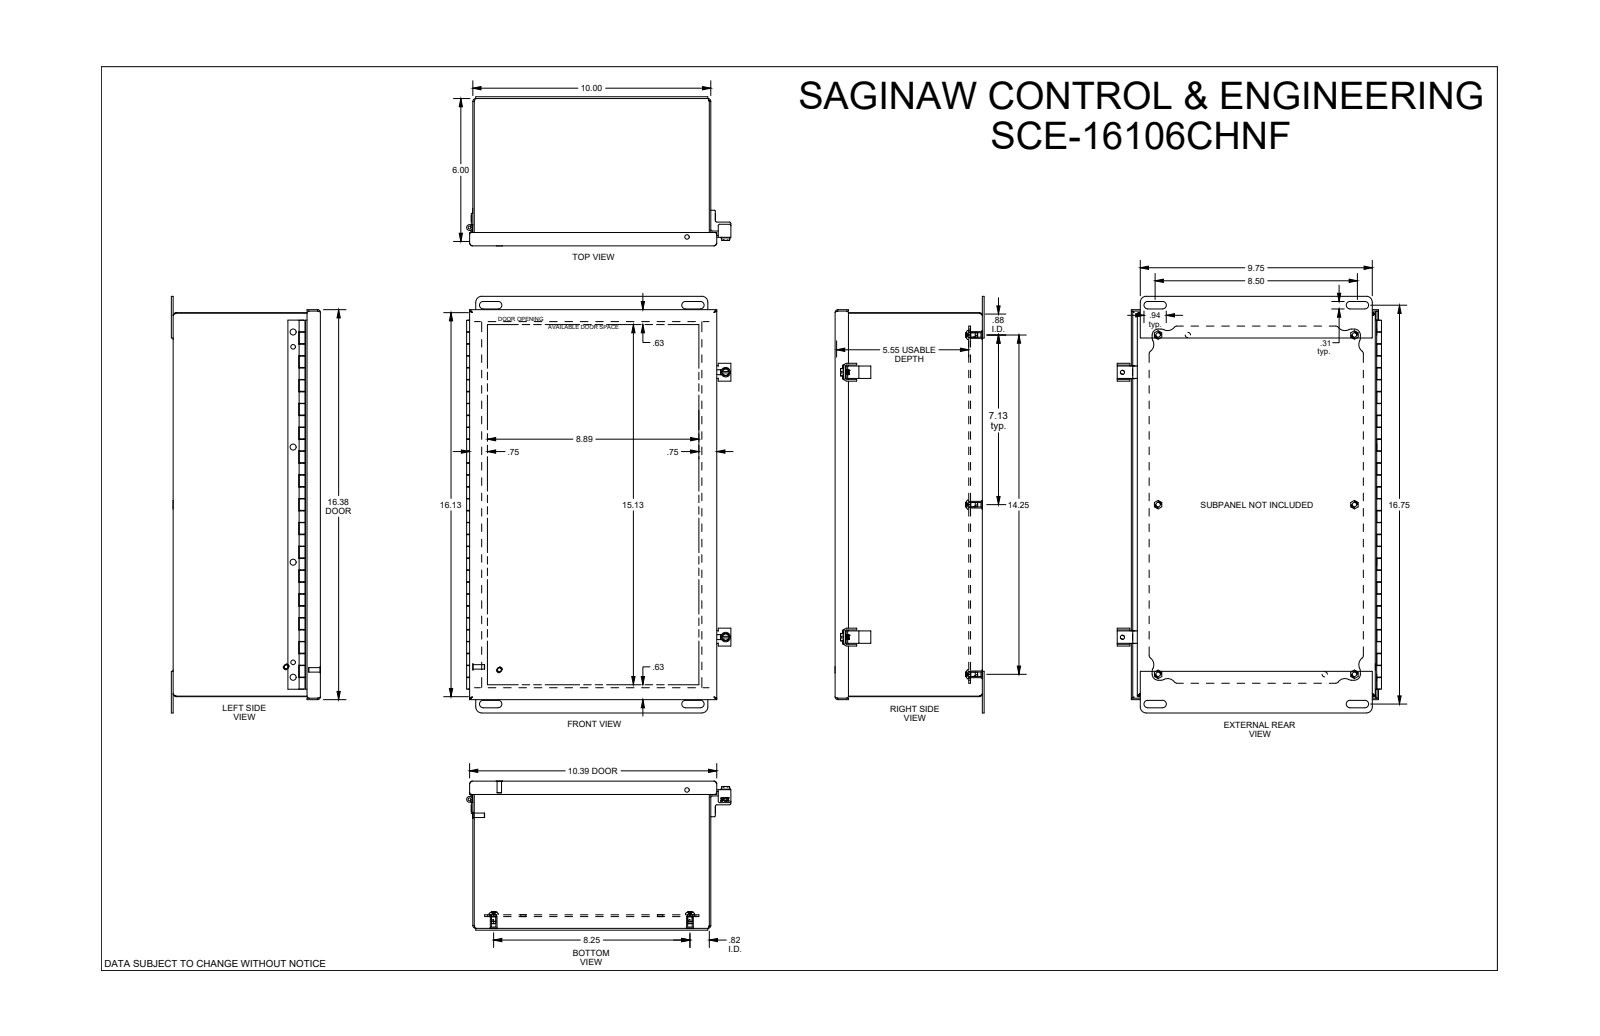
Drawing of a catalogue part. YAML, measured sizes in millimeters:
part_name: "SCE-16106CHNF"
step_written_by: "SolidWorks 2019 (AUTOMOTIVE_DESIGN)"
units: millimeters
bodies: {solids: 43, faces: 1472, planar: 656, cylindrical: 387, other: 429}
overall_size: [444.5, 282, 159.1]
volume: 969000
surface_area: 1194000
round_holes:
  - {diameter: 4.8, count: 12}
  - {diameter: 4.9, count: 8}
  - {diameter: 6.4, count: 6}
  - {diameter: 7.1, count: 4}
  - {diameter: 4, count: 2}
  - {diameter: 5.5, count: 2}
  - {diameter: 6.8, count: 2}
  - {diameter: 3.2, count: 1}
  - {diameter: 4.7, count: 1}
round_bosses_or_shafts:
  - {diameter: 4.8, count: 14}
  - {diameter: 6.5, count: 8}
  - {diameter: 9.5, count: 6}
  - {diameter: 7.1, count: 6}
  - {diameter: 10.1, count: 2}
  - {diameter: 4.8, count: 2}
  - {diameter: 6.2, count: 1}
  - {diameter: 3.1, count: 1}
partial_cylinders:
  - {radius: 0.3, count: 82}
  - {radius: 1.5, count: 33}
  - {radius: 6.4, count: 16}
  - {radius: 1.3, count: 8}
  - {radius: 3.2, count: 8}
  - {radius: 4, count: 8}
  - {radius: 8.7, count: 8}
  - {radius: 0.7, count: 6}
face_to_face_distances: [1.5, 155.6, 252.5, 157.1, 154.1, 1.9, 13, 11, 14.5, 141.1]
hole_center_spacings: [276.9, 361.9, 418.2, 181, 181, 362, 209.6, 276.9]
